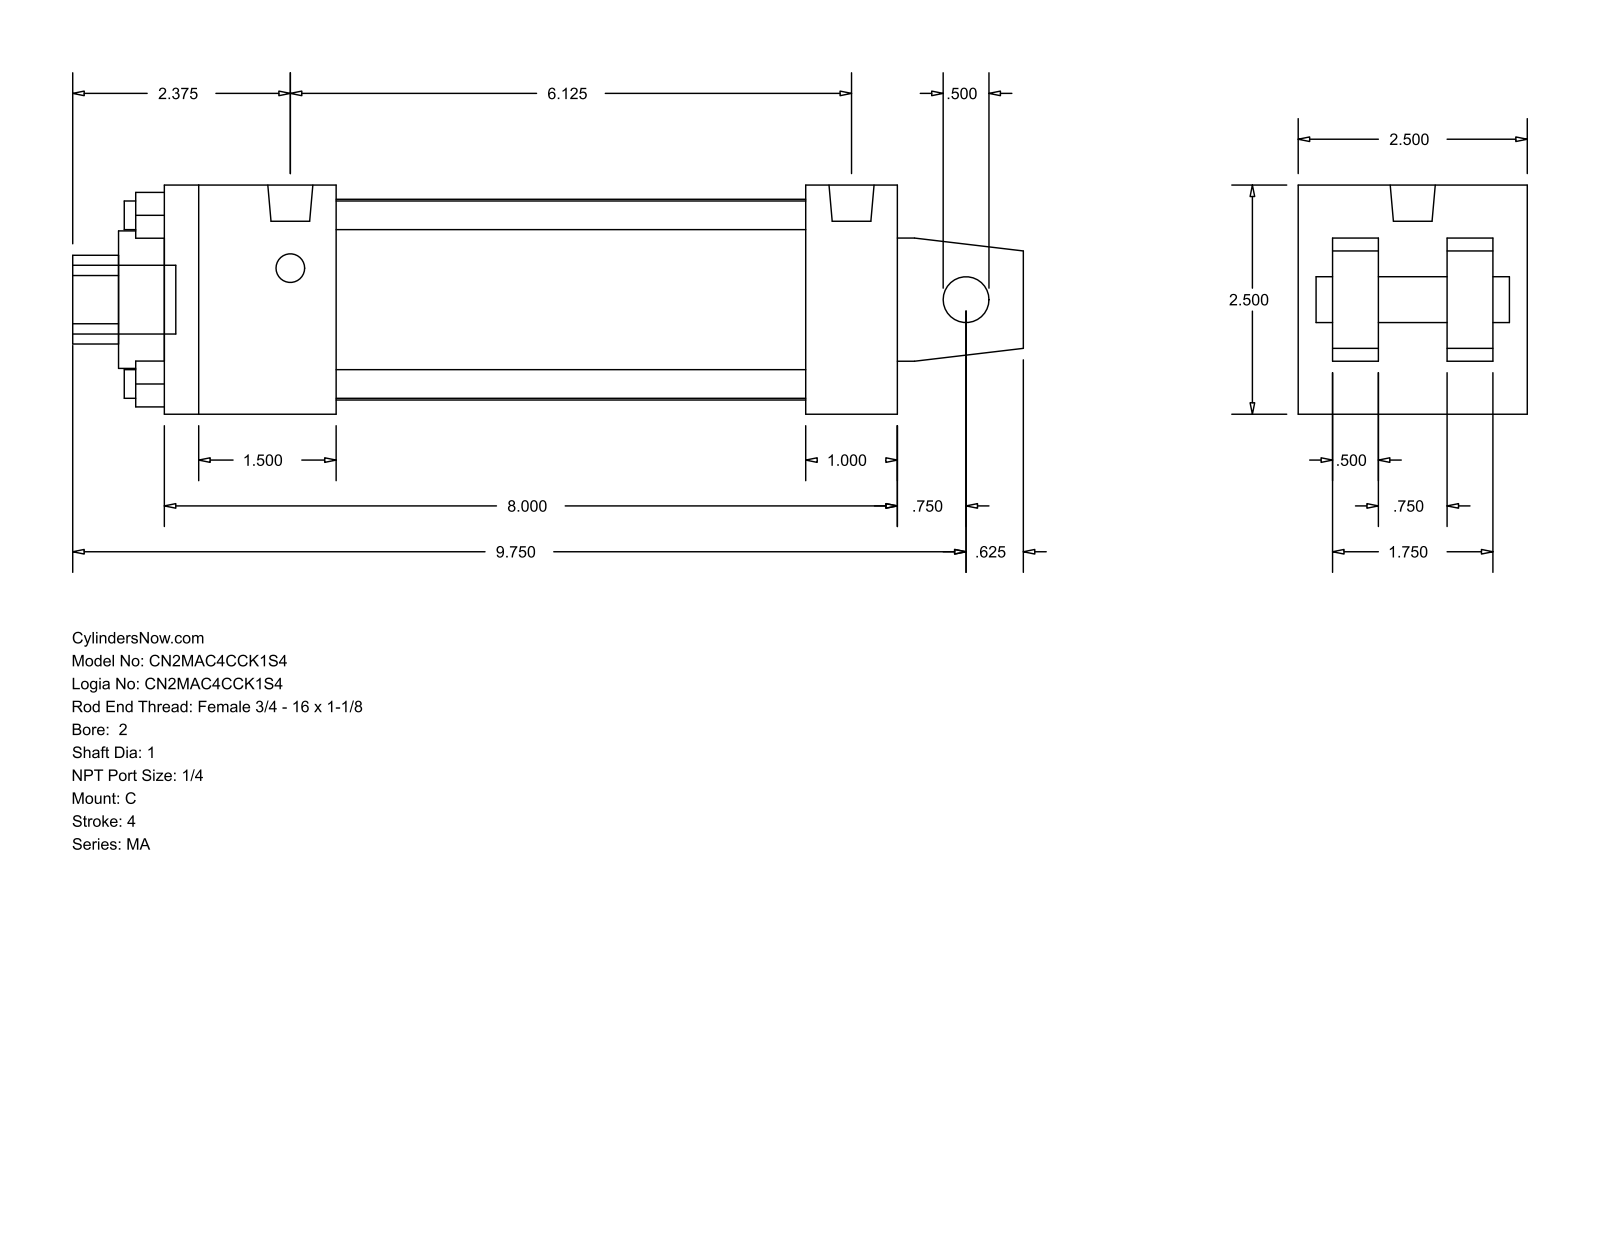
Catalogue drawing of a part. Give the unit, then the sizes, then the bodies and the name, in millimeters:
Units: millimetres
Overall size (bounding box): 263.52 × 63.5 × 63.5
Round holes (diameter × count): ⌀7.94 ×4, ⌀12.7 ×1, ⌀25.4 ×1, ⌀38.1 ×1, ⌀55.63 ×1
Round bosses / shafts (diameter × count): ⌀7.94 ×4, ⌀12.49 ×2, ⌀19.05 ×1
Partial cylindrical surfaces — rounded edges, fillets, slot ends (radius × count): R12.29 ×1
Main face-to-face distances: 63.5, 12.7, 203.2, 22.22, 41.28, 9.52, 53.98, 31.76, 47.63, 25.4
Hole centre spacings: 33.05, 46.74, 66.1
Bodies: 0 solids, 103 faces (76 planar, 27 cylindrical, 0 other)
Part name (STEP PRODUCT): MA_C__0200_1
STEP written by: GSSL Pune (CONFIG_CONTROL_DESIGN)
